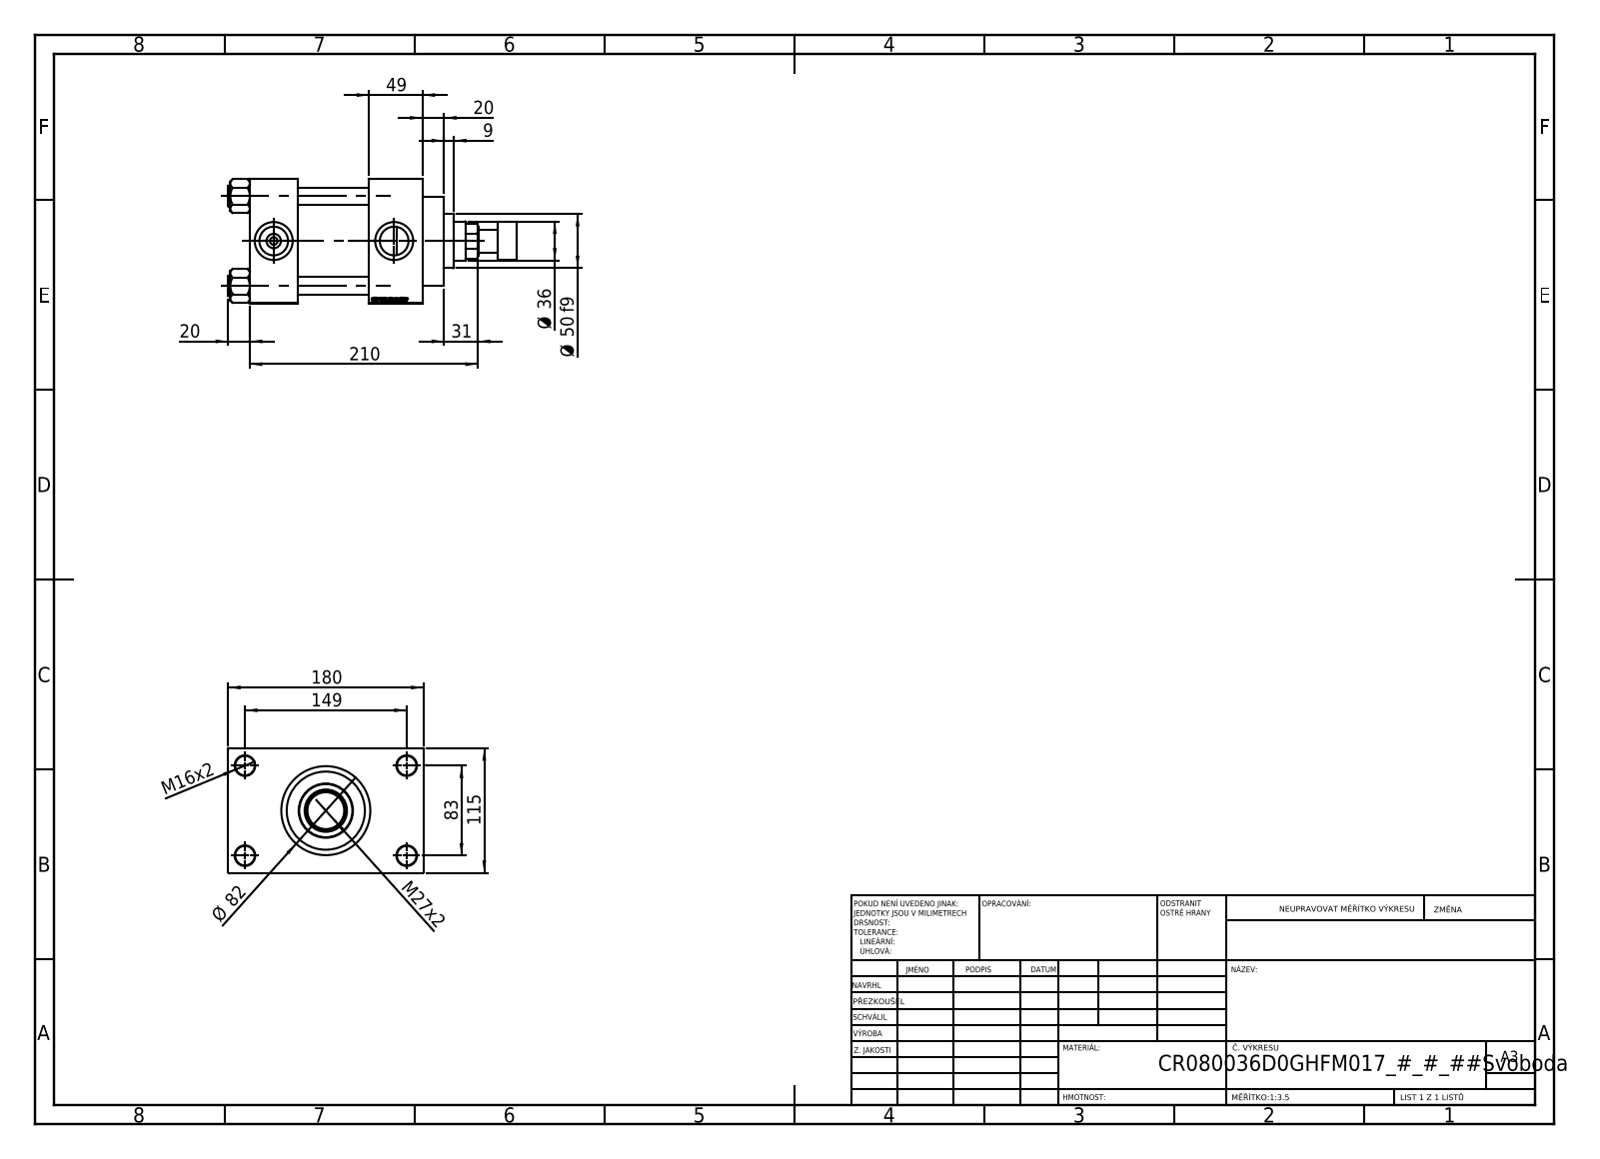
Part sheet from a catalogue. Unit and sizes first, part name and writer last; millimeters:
Units: millimetres
Overall size (bounding box): 266 × 180 × 115
Round holes (diameter × count): ⌀16 ×4, ⌀18 ×4, ⌀7 ×2, ⌀26.44 ×2, ⌀35 ×2, ⌀25.5 ×1, ⌀36 ×1, ⌀39 ×1, ⌀61 ×1, ⌀72 ×1, ⌀80 ×1
Round bosses / shafts (diameter × count): ⌀19 ×4, ⌀86 ×1, ⌀82 ×1, ⌀50 ×1, ⌀35 ×1, ⌀21 ×1
Main face-to-face distances: 115, 66, 49, 110, 44, 159, 32.5, 147.5, 20, 69
Hole centre spacings: 33.15, 58.48, 82.7, 85.28, 89.24, 115.85, 142.43, 83
Volume: 2 003 000 mm³ · Surface area: 302 161 mm²
Bodies: 12 solids, 1165 faces (549 planar, 92 cylindrical, 524 other)
Part name (STEP PRODUCT): V215CR_D_TYCINKA; V215_VC_A; V215CR_ROD_END_F; NUT_M5_D (+2 more)
STEP written by: SolidWorks 2019 (CONFIG_CONTROL_DESIGN)
